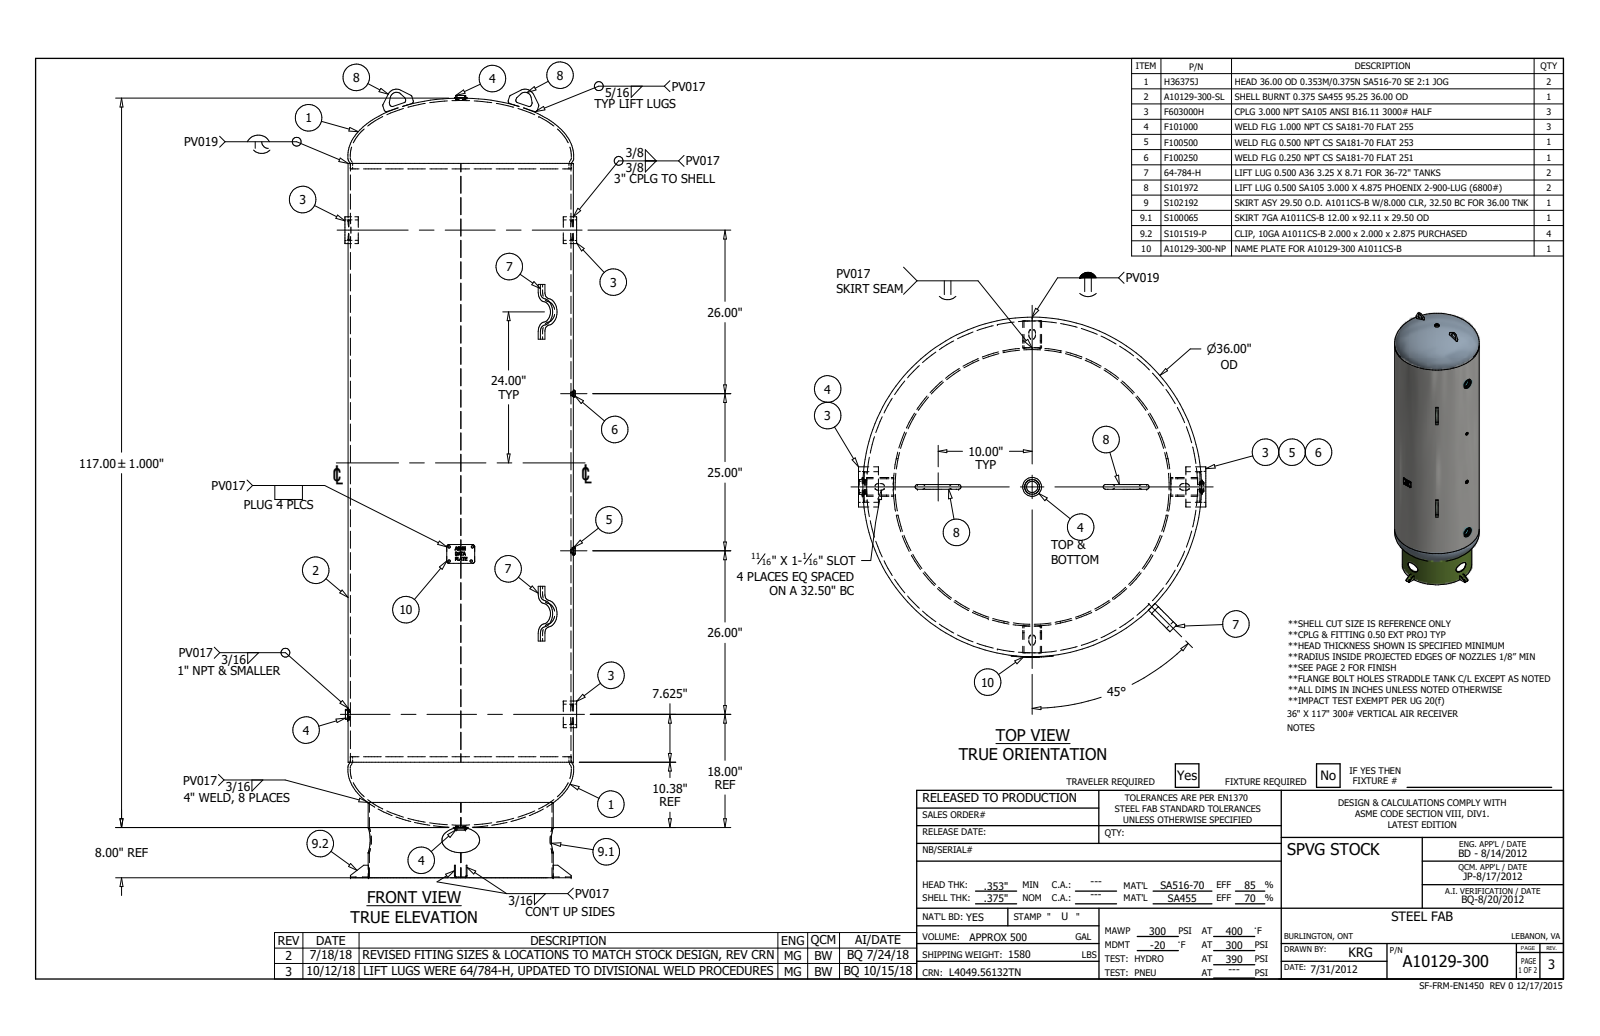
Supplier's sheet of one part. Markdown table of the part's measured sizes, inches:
| quantity | value |
| --- | --- |
| part name | A10129-300; H36375J; A10129-300-SL; F603000H (+8 more) |
| STEP written by | Autodesk Inventor 2019 (AUTOMOTIVE_DESIGN) |
| units | inches |
| bodies | 27 solids, 463 faces (244 planar, 119 cylindrical, 100 other) |
| overall size | 125.427 × 36.929 × 36.06 |
| volume | 5 443 in³ |
| surface area | 30 539 in² |
| round holes (diameter × count) | 0.375 × 4, 0.5 × 2, 1.193 × 2, 3 × 2, 3.25 × 2, 0.451 × 1, 0.734 × 1, 1 × 1, 29.125 × 1, 34.5 × 1, 35.179 × 1, 35.25 × 1 |
| round bosses / shafts (diameter × count) | 4.25 × 2, 2 × 2, 1.563 × 2, 0.5 × 2, 35.929 × 1, 29.5 × 1, 1.063 × 1 |
| partial cylindrical surfaces (radius × count) | 0.25 × 16, 0.344 × 8, 0.187 × 4, 0.322 × 4, 0.375 × 4, 1 × 4, 1.5 × 4, 7.37 × 4 |
| main face-to-face distances | 95.25, 0.875, 94.375, 93.5, 94.375, 0.875, 0.135, 18.375, 19.25, 112.75 |
| hole center spacings | 26, 51, 2.25, 2.258, 3.528, 3.716, 4.184, 4.344 |
